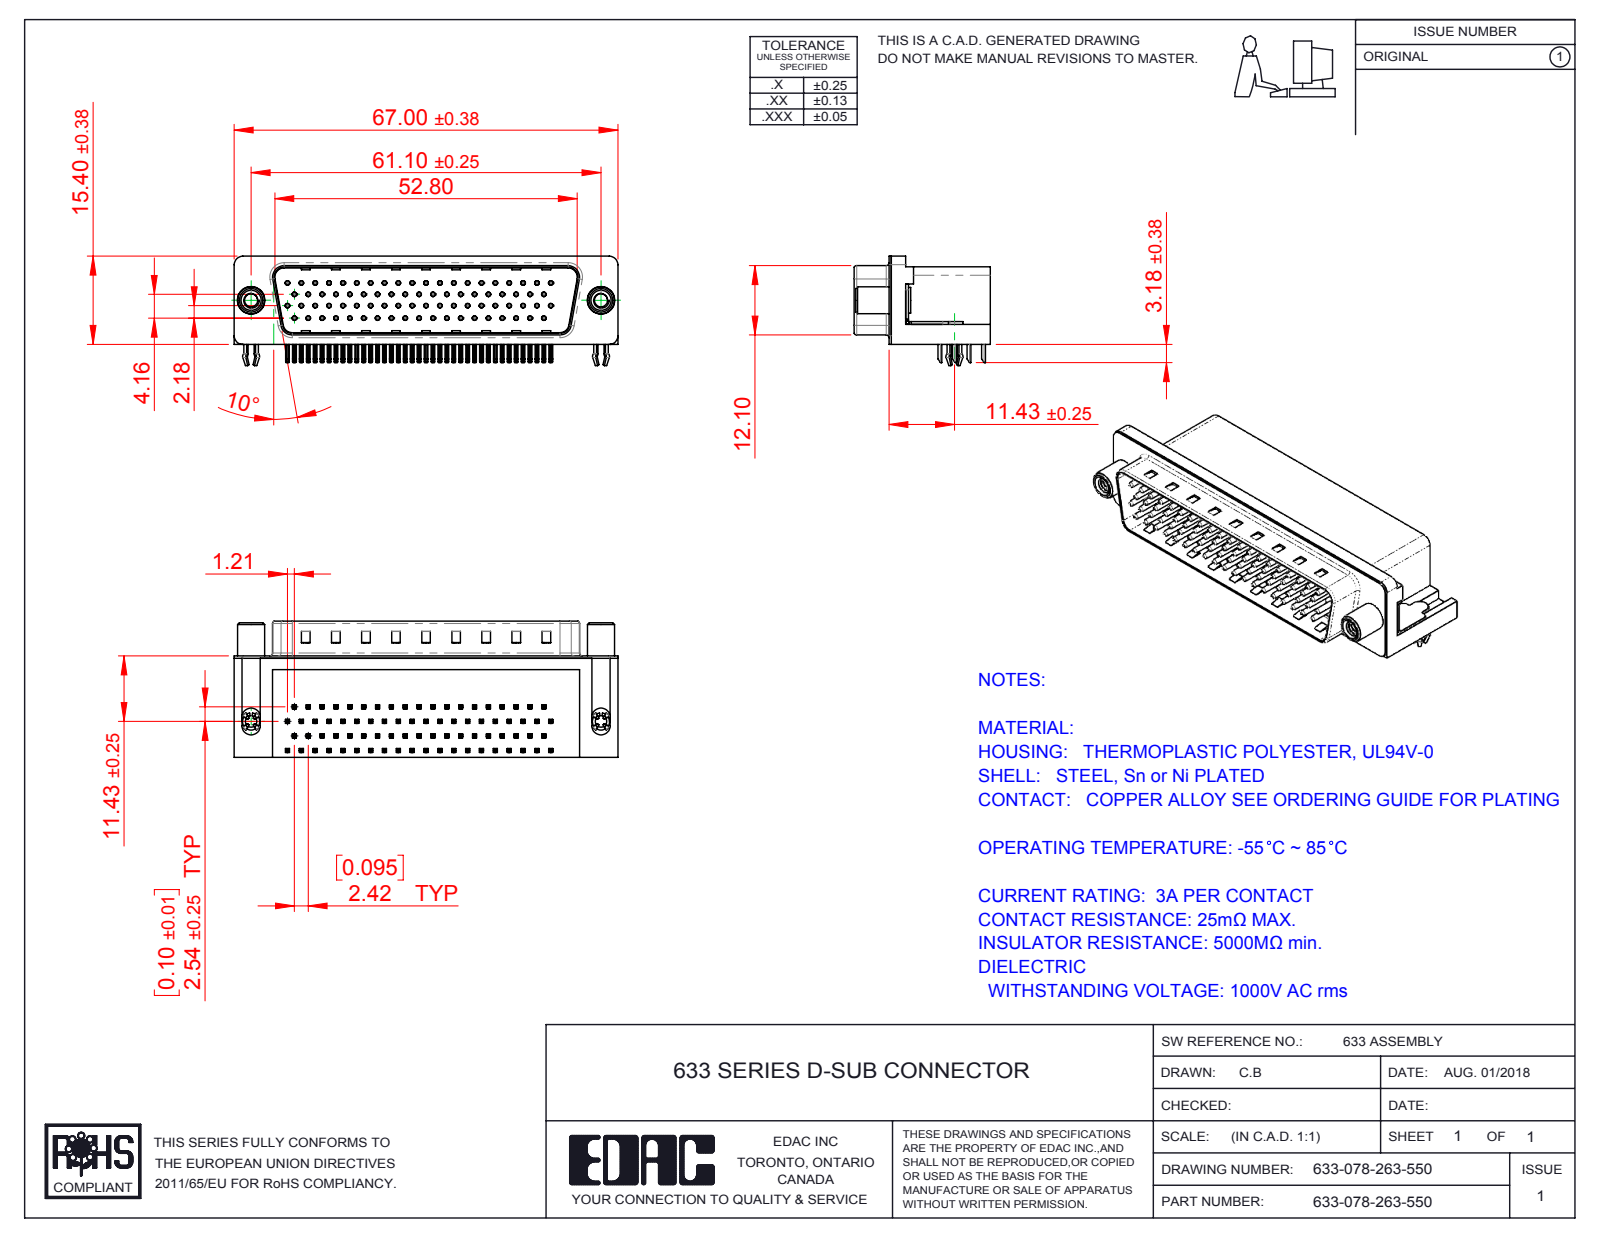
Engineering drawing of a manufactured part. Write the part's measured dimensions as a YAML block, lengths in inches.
part_name: "633 Round Threaded Standoff; 633-078-263-550; 633 4 Prong Board Lock_78 Contact; 633 Contact Top 78 (+5 more)"
step_written_by: "SolidWorks 2016 (CONFIG_CONTROL_DESIGN)"
units: inches
bodies: {solids: 84, faces: 6390, planar: 4015, cylindrical: 1792, other: 583}
overall_size: [2.638, 0.937, 0.752]
volume: 0.898
surface_area: 25.77
round_holes:
  - {diameter: 0.014, count: 78}
  - {diameter: 0.031, count: 78}
  - {diameter: 0.079, count: 2}
  - {diameter: 0.091, count: 2}
  - {diameter: 0.122, count: 2}
  - {diameter: 0.157, count: 2}
  - {diameter: 0.189, count: 2}
  - {diameter: 0.197, count: 2}
round_bosses_or_shafts:
  - {diameter: 0.03, count: 78}
  - {diameter: 0.193, count: 2}
  - {diameter: 0.185, count: 2}
  - {diameter: 0.177, count: 2}
  - {diameter: 0.152, count: 2}
  - {diameter: 0.118, count: 2}
partial_cylinders:
  - {radius: 0.01, count: 316}
  - {radius: 0.005, count: 156}
  - {radius: 0.039, count: 16}
  - {radius: 0.02, count: 9}
  - {radius: 0.063, count: 8}
  - {radius: 0.059, count: 6}
  - {radius: 0.018, count: 4}
  - {radius: 0.035, count: 4}
face_to_face_distances: [0.016, 0.52, 0.681, 0.461, 0.526, 0.081, 0.541, 0.065, 0.073, 0.469]
hole_center_spacings: [0.095, 0.191, 0.286, 0.381, 0.246, 0.281, 0.476, 0.339]
